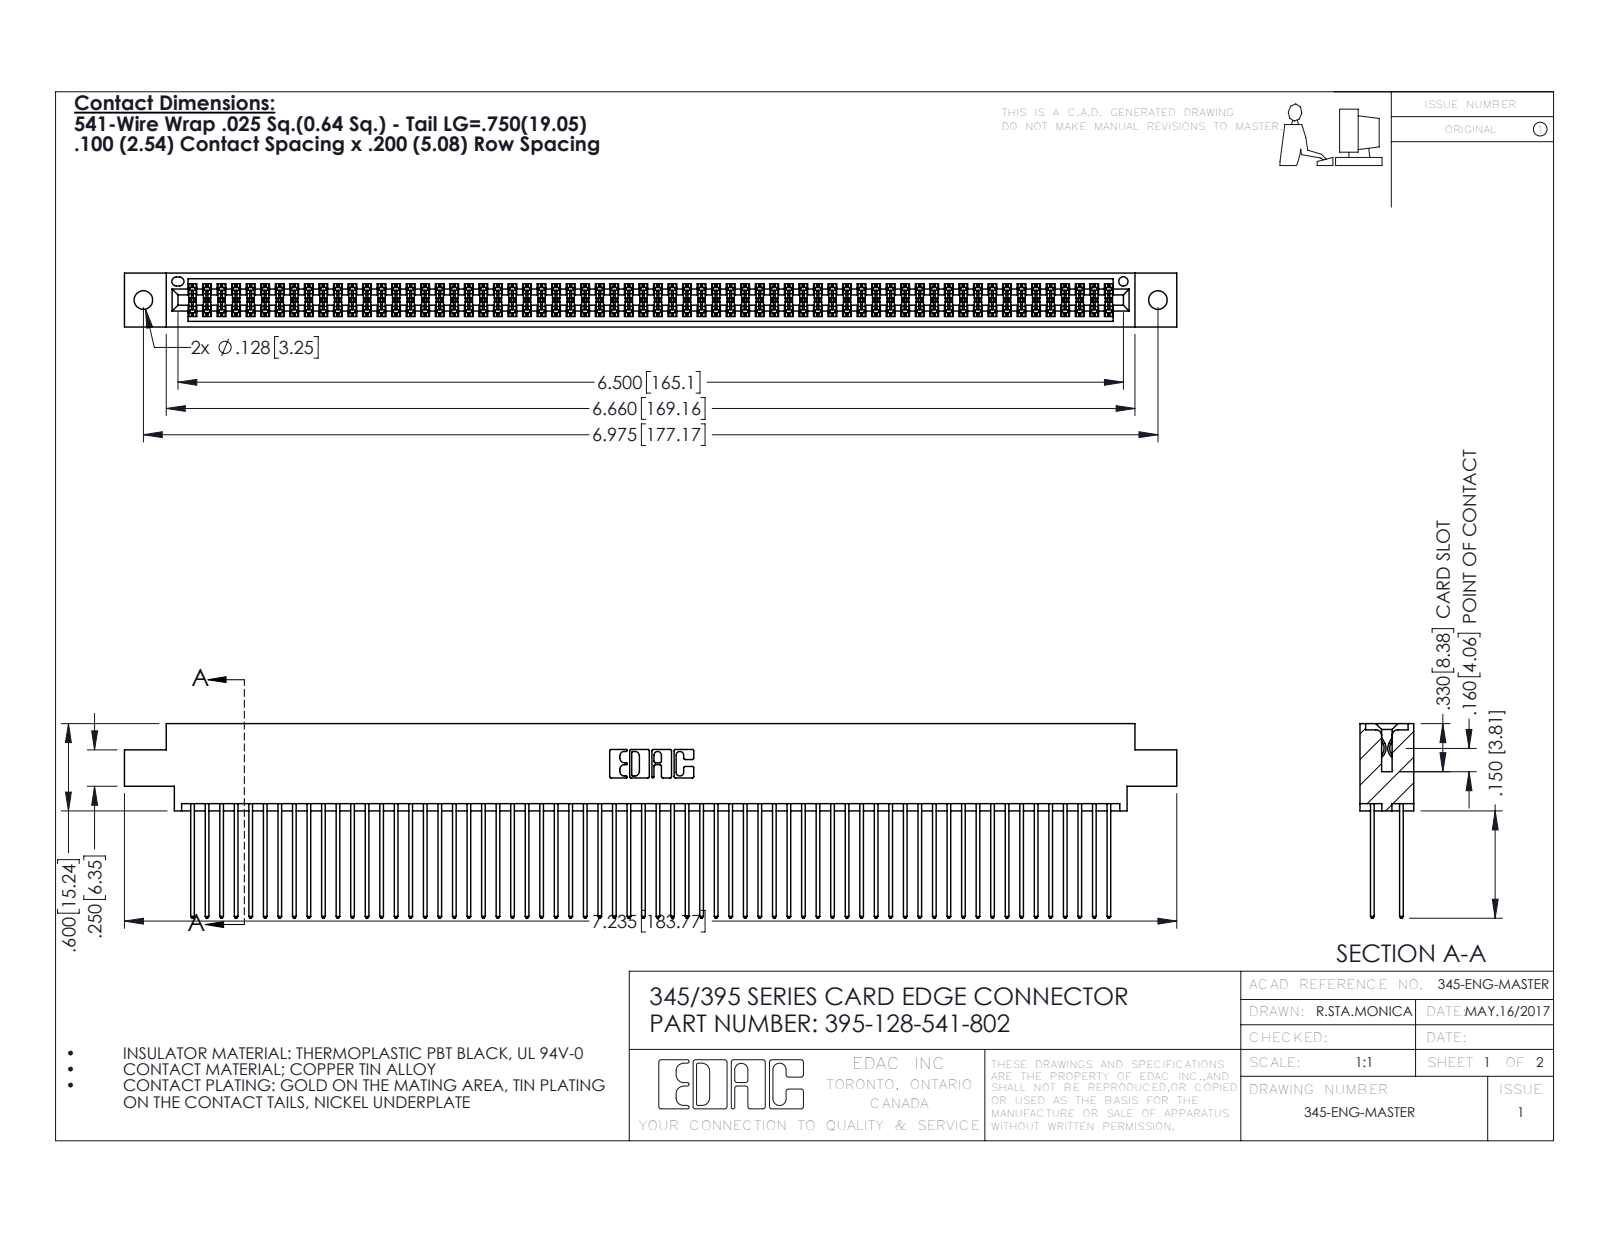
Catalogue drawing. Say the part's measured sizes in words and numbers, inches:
The part is named "395-128-541-802; 345-292-001_345-293-141; 345 Part_0.170 Offset - 0.128 Dia". Its 3-D file was written by "SolidWorks 2016 (CONFIG_CONTROL_DESIGN)". It is 129 solids with 6530 faces: 4308 planar, 2222 cylindrical and 0 other. Overall it measures 7.235 by 1.337 by 0.37 inches. Its volume is 1.137 cubic inches and its surface area 48.52 square inches. Round holes: 2 of diameter 0.128, 1 of diameter 0.064. Partial cylindrical surfaces (rounded edges, fillets, slot ends): 192 of radius 0.006, 128 of radius 0.01, 22 of radius 0.01, 6 of radius 0.007, 6 of radius 0.031, 3 of radius 0.026, 2 of radius 0.014, 2 of radius 0.019. The main face-to-face distances are 0.298, 0.072, 0.2, 0.098, 0.272, 0.025, 0.225, 0.37, 0.175, 0.149. The hole center spacings are 0.27, 6.739, 6.975.
